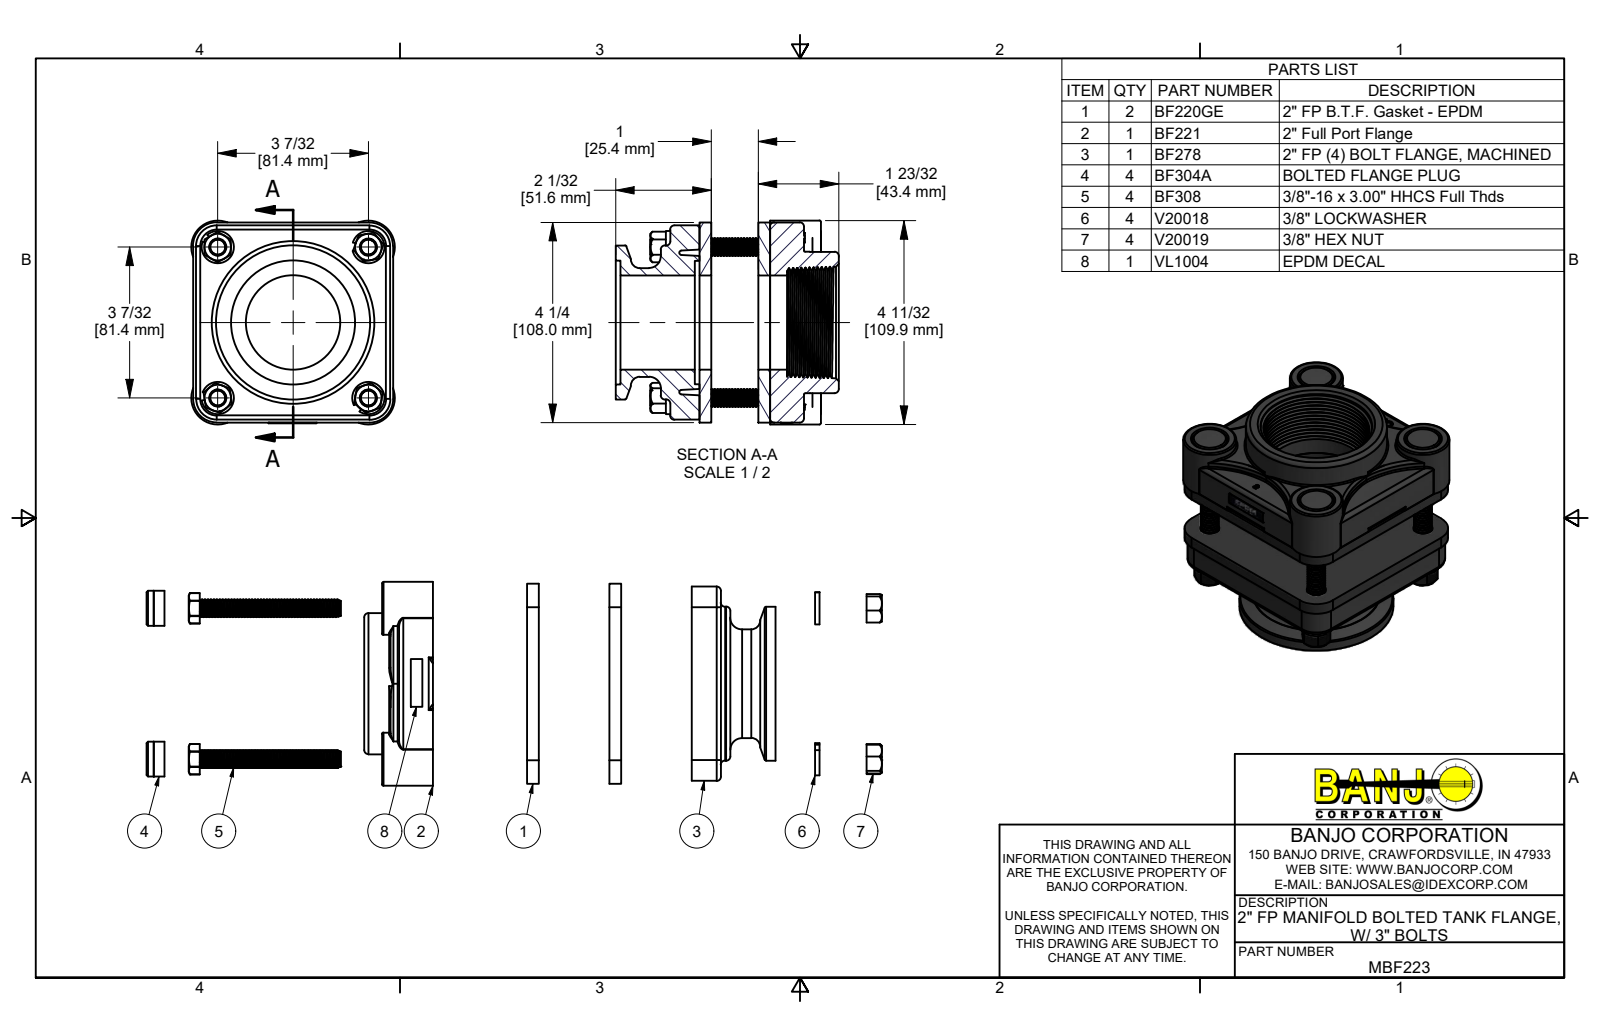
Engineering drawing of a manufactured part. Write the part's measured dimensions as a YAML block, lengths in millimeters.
part_name: "MBF223; BF221; BF221BD; BF278 (+7 more)"
step_written_by: "Autodesk Inventor 2019 (AUTOMOTIVE_DESIGN)"
units: millimeters
bodies: {solids: 21, faces: 1583, planar: 283, cylindrical: 600, other: 700}
overall_size: [970.6, 109.9, 109.9]
volume: 546800
surface_area: 343800
round_holes:
  - {diameter: 7.8, count: 4}
  - {diameter: 9.5, count: 4}
  - {diameter: 9.7, count: 4}
  - {diameter: 9.8, count: 4}
  - {diameter: 10.4, count: 4}
  - {diameter: 11.1, count: 4}
  - {diameter: 18.3, count: 4}
  - {diameter: 18.9, count: 4}
  - {diameter: 50.8, count: 1}
  - {diameter: 66.5, count: 1}
  - {diameter: 66.8, count: 1}
round_bosses_or_shafts:
  - {diameter: 8.2, count: 188}
  - {diameter: 28.6, count: 4}
  - {diameter: 18.8, count: 4}
  - {diameter: 17.4, count: 4}
  - {diameter: 9.5, count: 4}
  - {diameter: 83.1, count: 1}
  - {diameter: 76.2, count: 1}
  - {diameter: 58.7, count: 1}
partial_cylinders:
  - {radius: 2.3, count: 12}
  - {radius: 0.8, count: 8}
  - {radius: 1.5, count: 8}
  - {radius: 4.1, count: 8}
  - {radius: 50.8, count: 8}
  - {radius: 8.2, count: 4}
  - {radius: 11.2, count: 4}
  - {radius: 12.7, count: 4}
face_to_face_distances: [6.4, 31.8, 38.1, 25.4, 1.6, 106.3, 108, 15.7, 22.1, 47.5]
hole_center_spacings: [81.4, 57.5, 57.5, 81.4, 81.4, 115.1, 115.1, 115.1]
